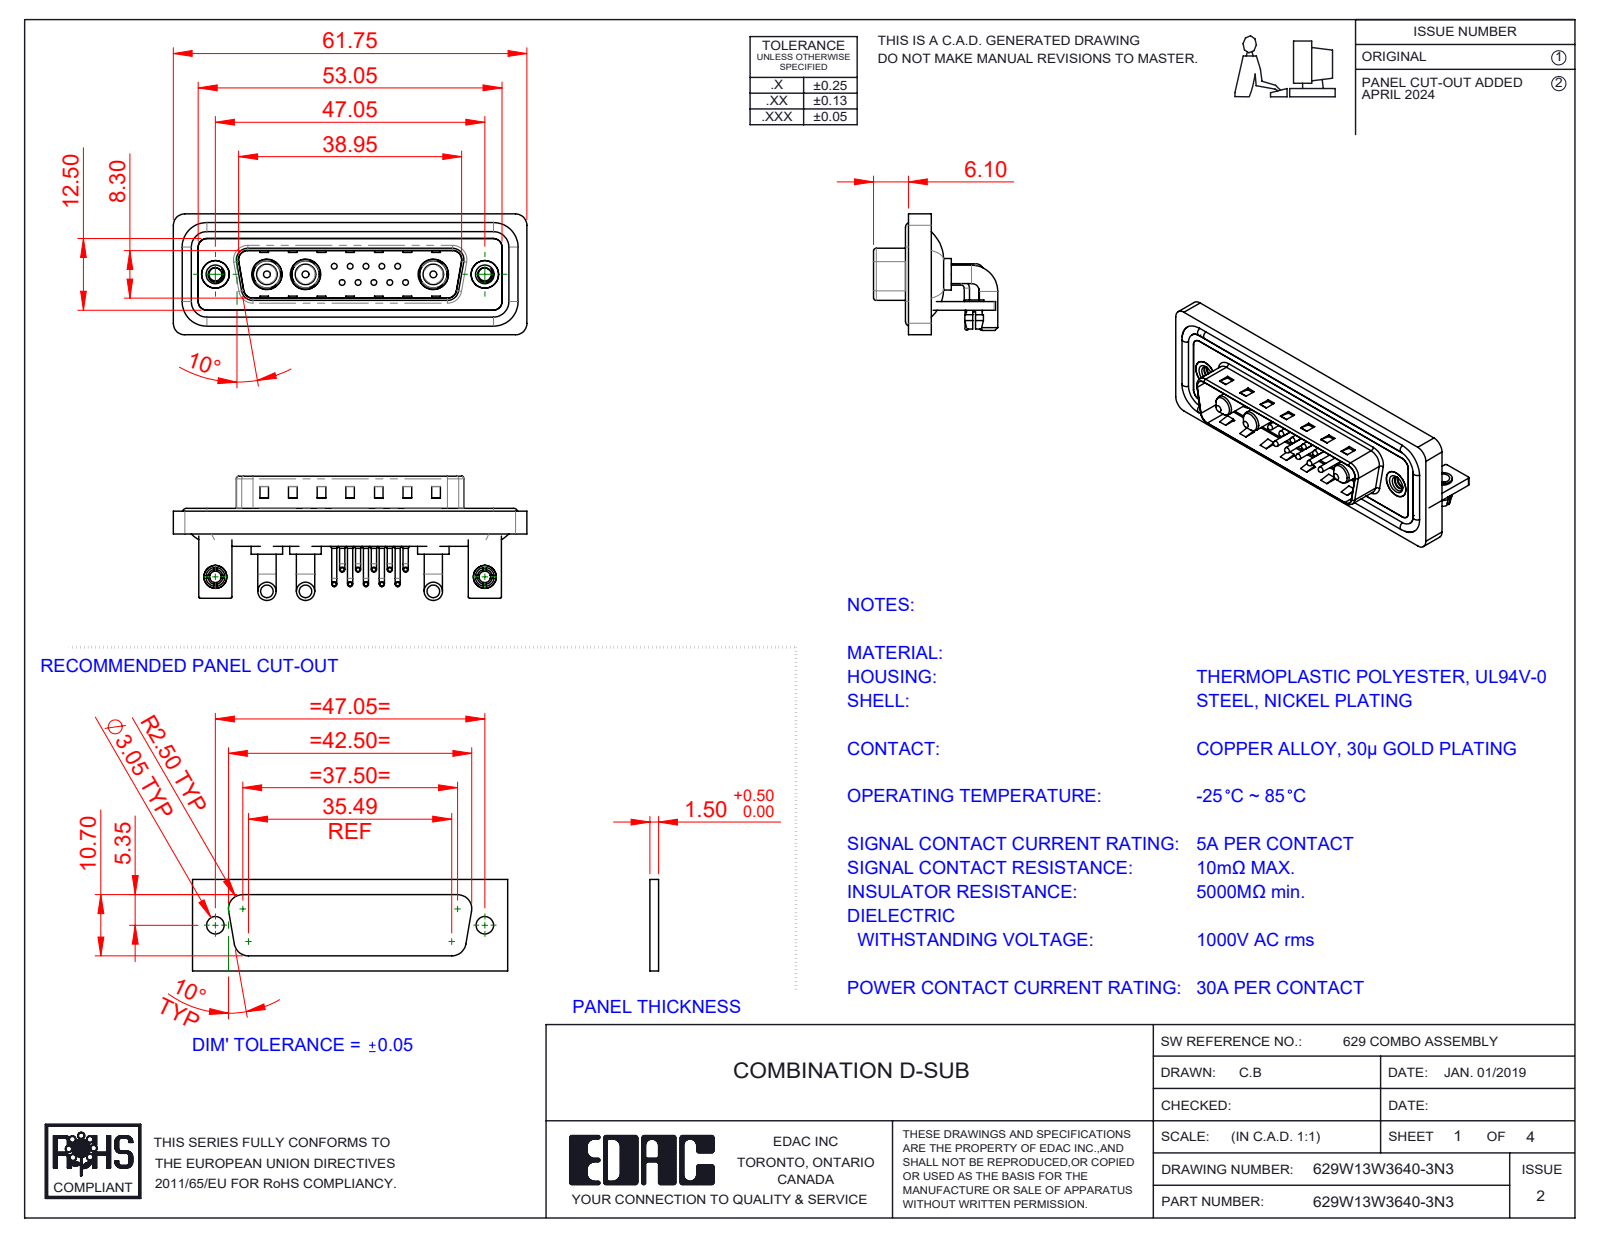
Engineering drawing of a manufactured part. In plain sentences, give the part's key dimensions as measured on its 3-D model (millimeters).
The part is named "629Combo Shell Rear_25 Contacts; 629Combo Threaded Rivet_3; 629W13W3640-3N3; 629Combo Waterproof Housing_25 Contacts (+7 more)". Its 3-D file was written by "SolidWorks 2023 (CONFIG_CONTROL_DESIGN)". It is 27 solids with 1844 faces: 947 planar, 661 cylindrical and 236 other. Overall it measures 61.75 by 21.7 by 21.1 millimeters. Its volume is 8 008 cubic millimeters and its surface area 13 349 square millimeters. Round holes: 12 of diameter 2, 10 of diameter 0.75, 10 of diameter 1.6, 3 of diameter 4.85, 3 of diameter 5.3, 2 of diameter 2.26, 2 of diameter 2.5, 2 of diameter 3.2, 2 of diameter 4, 2 of diameter 4.8, 2 of diameter 5. Round bosses or shafts: 20 of diameter 0.9, 10 of diameter 1.5, 10 of diameter 1, 10 of diameter 0.65, 6 of diameter 3.2, 4 of diameter 1.6, 3 of diameter 5.5, 3 of diameter 5.2. Partial cylindrical surfaces (rounded edges, fillets, slot ends): 19 of radius 2, 18 of radius 1.5, 16 of radius 0.25, 10 of radius 1.01, 9 of radius 0.5, 8 of radius 1.6, 4 of radius 0.6, 4 of radius 0.65. The main face-to-face distances are 0.4, 0.8, 1.5, 2.9, 2.1, 1.1, 4.1, 1.6, 3.7, 4.5. The hole center spacings are 3.16, 2.77, 5.04, 5.54, 7.49, 5.03, 8.31, 10.11.
